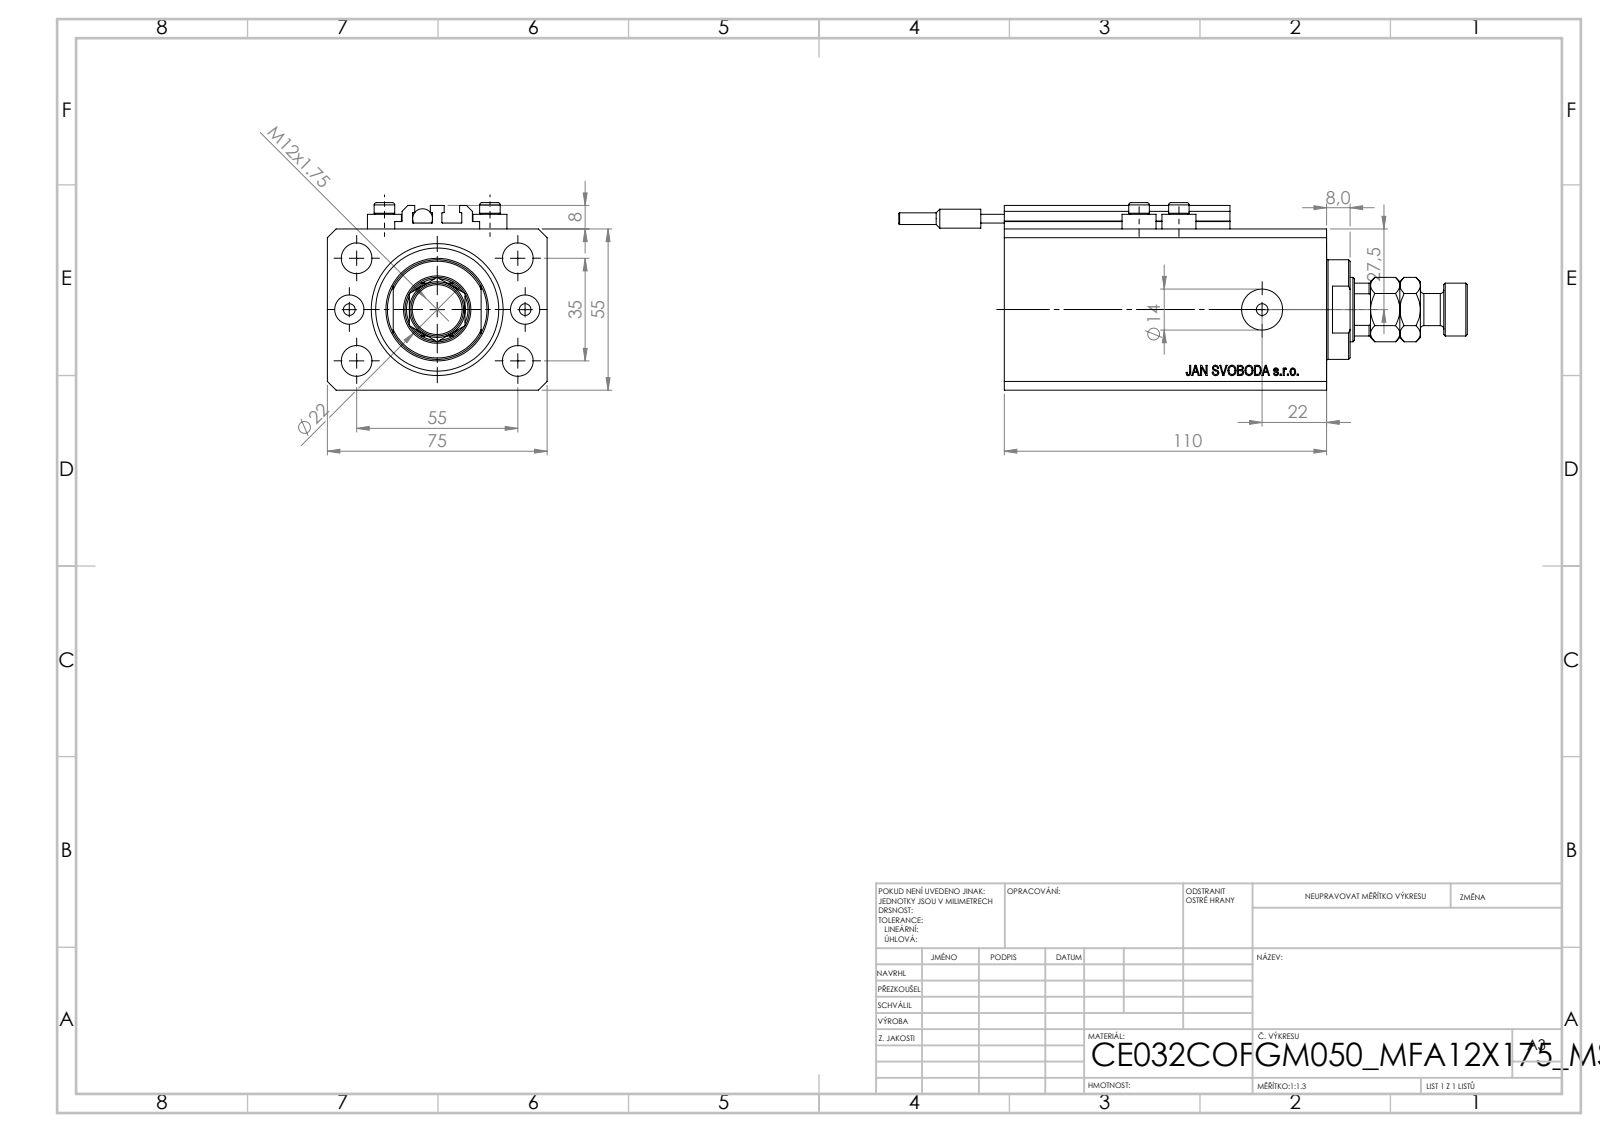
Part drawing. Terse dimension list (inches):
name: MFA; SWITCH_V250CE; V250CE_C_Body; V250CE_VC_C (+2 more)
written by: SolidWorks 2019 (CONFIG_CONTROL_DESIGN)
unit: in
bodies: 10 solids, 1111 faces (535 planar, 96 cylindrical, 480 other)
size: 7.634 × 2.953 × 2.52
volume: 25.55 in³; area: 151.7 in²
holes: 8× ⌀0.157, 5× ⌀0.413, 2× ⌀0.394, 2× ⌀0.551, 1× ⌀0.866, 1× ⌀1.26, 1× ⌀1.772
bosses: 4× ⌀0.457, 4× ⌀0.276, 1× ⌀1.339, 1× ⌀0.709, 1× ⌀0.433, 1× ⌀0.268, 1× ⌀0.256, 1× ⌀0.157
rounds: 10× R0.008, 1× R0.413
face distances: 2.165, 2.953, 4.331, 3.264, 1.067, 0.39, 2.874, 3.941, 0.098, 0.118
hole spacings: 0.696, 1.283, 2.366, 0.535, 1.181, 1.378, 1.417, 1.515
